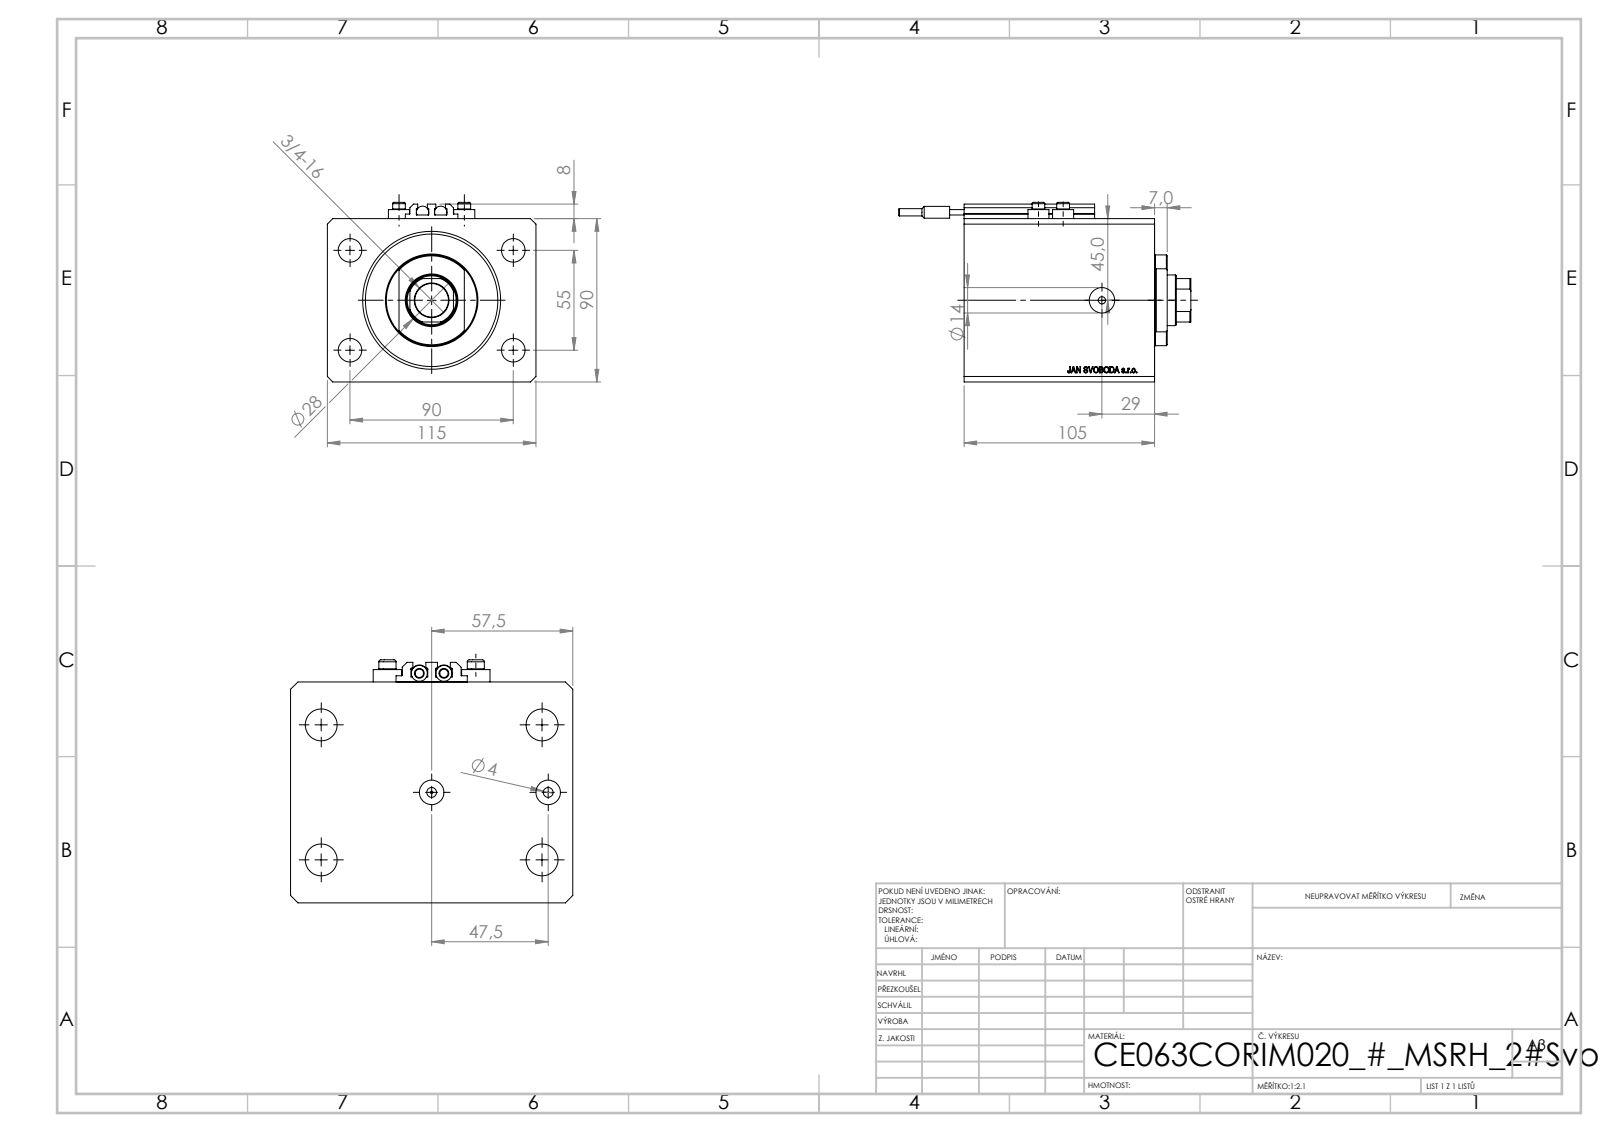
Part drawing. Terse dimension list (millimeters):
name: V250CE_C_VCP; V250CE_C_Body; V250CE_VC_C; SWITCH_V250CE (+1 more)
written by: SolidWorks 2019 (CONFIG_CONTROL_DESIGN)
unit: mm
bodies: 10 solids, 1090 faces (536 planar, 100 cylindrical, 454 other)
size: 161 × 115 × 99
volume: 999 880 mm³; area: 150 933 mm²
holes: 8× ⌀4, 4× ⌀13, 2× ⌀10, 2× ⌀14, 1× ⌀1.25, 1× ⌀18.5, 1× ⌀28, 1× ⌀63, 1× ⌀76
bosses: 4× ⌀11.6, 4× ⌀7, 2× ⌀6.8, 2× ⌀6.5, 2× ⌀4, 1× ⌀50
rounds: 10× R0.2, 1× R13.5
face distances: 90, 115, 20, 105, 87.1, 17.9, 85, 67.1, 40, 65
hole spacings: 52.74, 13.6, 27.61, 36, 38.48, 55, 90, 96.5
